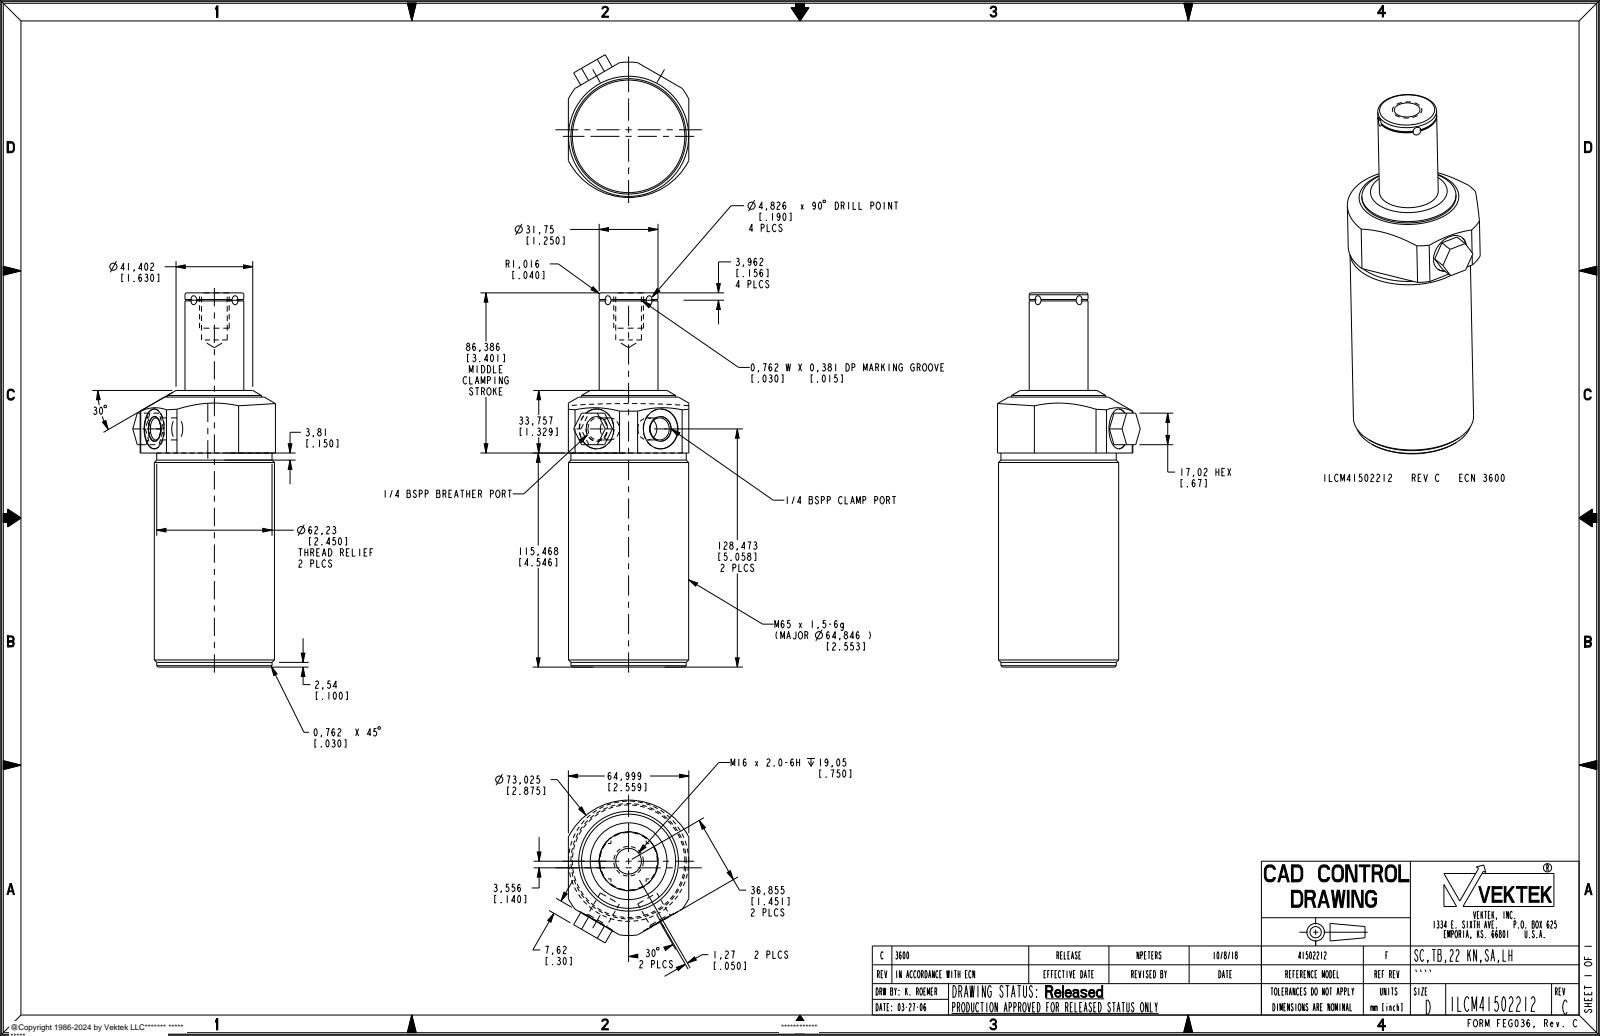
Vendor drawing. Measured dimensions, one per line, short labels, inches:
name: ILCM41502212
written by: PRO/ENGINEER BY PARAMETRIC TECHNOLOGY CORPORATION, 2013320 (AUTOMOTIVE_DESIGN)
unit: in
bodies: 1 solid, 92 faces (30 planar, 36 cylindrical, 26 other)
size: 7.947 × 3.032 × 2.559
volume: 32.66 in³; area: 72.6 in²
holes: 2× ⌀0.468, 2× ⌀0.524, 2× ⌀0.846, 1× ⌀0.546
bosses: 1× ⌀2.553, 1× ⌀2.45, 1× ⌀2, 1× ⌀1.25, 1× ⌀1.22, 1× ⌀0.63
rounds: 1× R1.437
face distances: 2.559, 4.546, 5.875, 1.329, 7.947, 3.401, 2.072, 0.31, 0.3, 5.734
